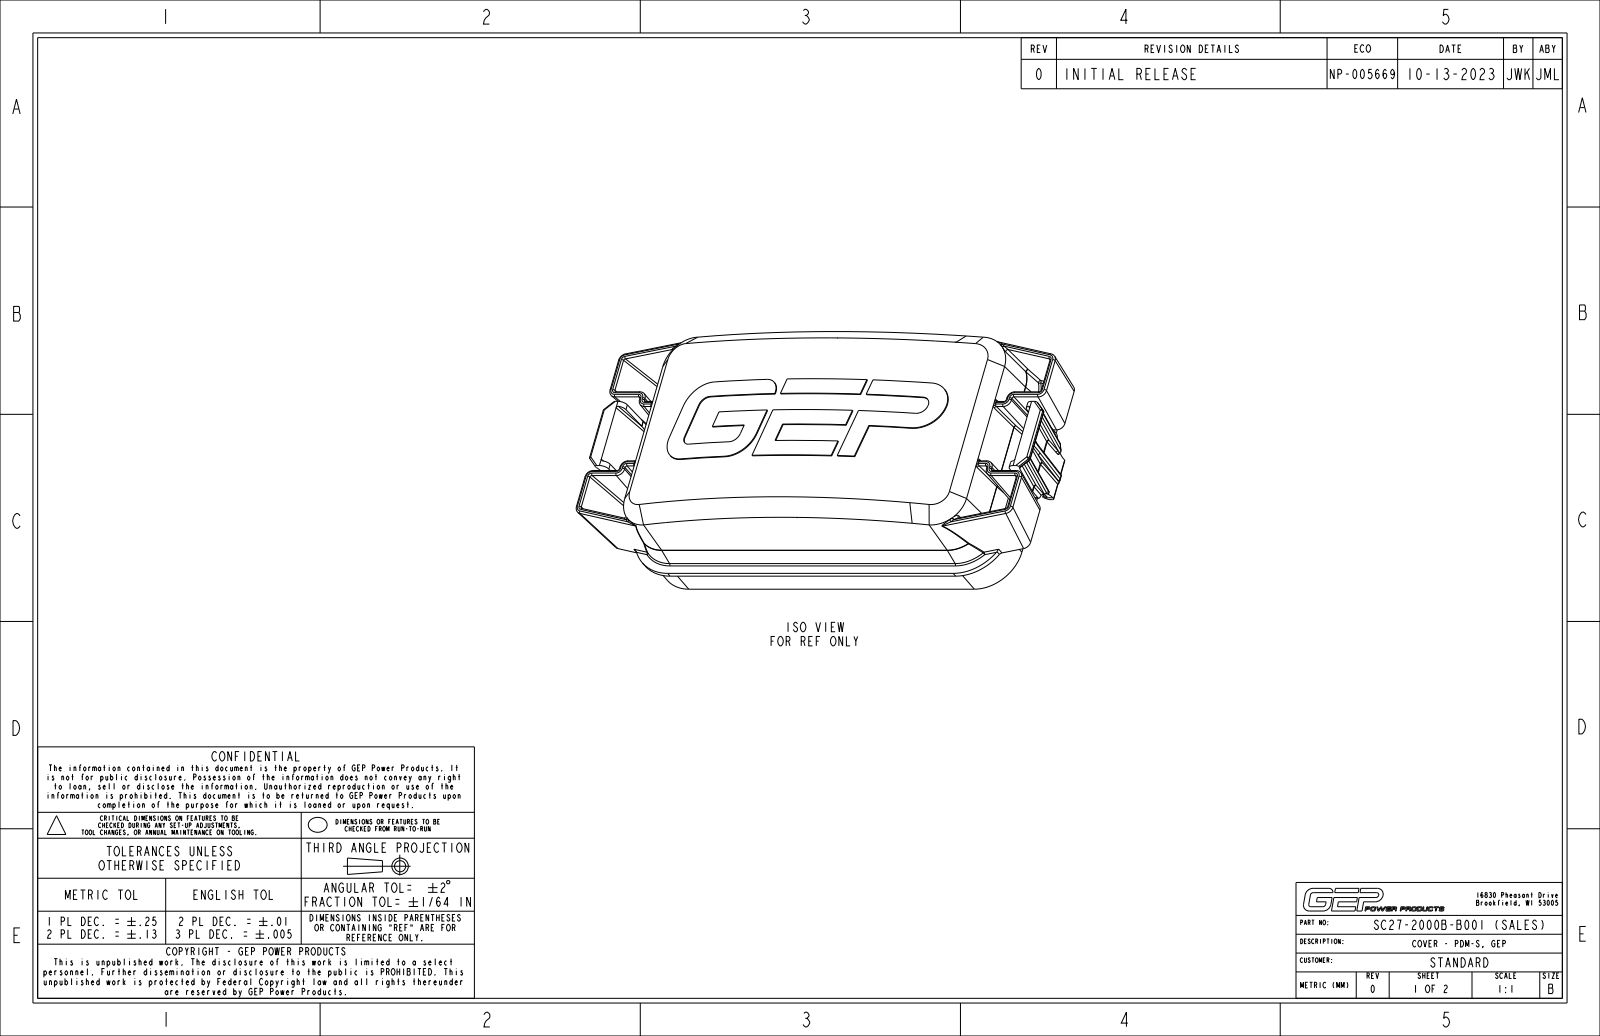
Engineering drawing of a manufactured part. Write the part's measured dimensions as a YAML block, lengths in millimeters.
part_name: "PC27-2000B-B001_NCF; SC27-2000B-B001_NCF_ASM"
step_written_by: "CREO PARAMETRIC BY PTC INC, 2017110 (CONFIG_CONTROL_DESIGN)"
units: millimeters
bodies: {solids: 1, faces: 1544, planar: 442, cylindrical: 429, other: 673}
overall_size: [136.9, 68.1, 37.5]
volume: 34473
surface_area: 45568
round_holes:
  - {diameter: 4, count: 1}
partial_cylinders:
  - {radius: 0.5, count: 224}
  - {radius: 2, count: 22}
  - {radius: 1, count: 19}
  - {radius: 1.7, count: 8}
  - {radius: 0.4, count: 4}
  - {radius: 0.52, count: 4}
  - {radius: 0.6, count: 4}
  - {radius: 10, count: 4}
face_to_face_distances: [1.5, 62.6, 8.05, 56.05, 6.55, 54.55, 1.2, 64.1, 6.85, 57.25]
